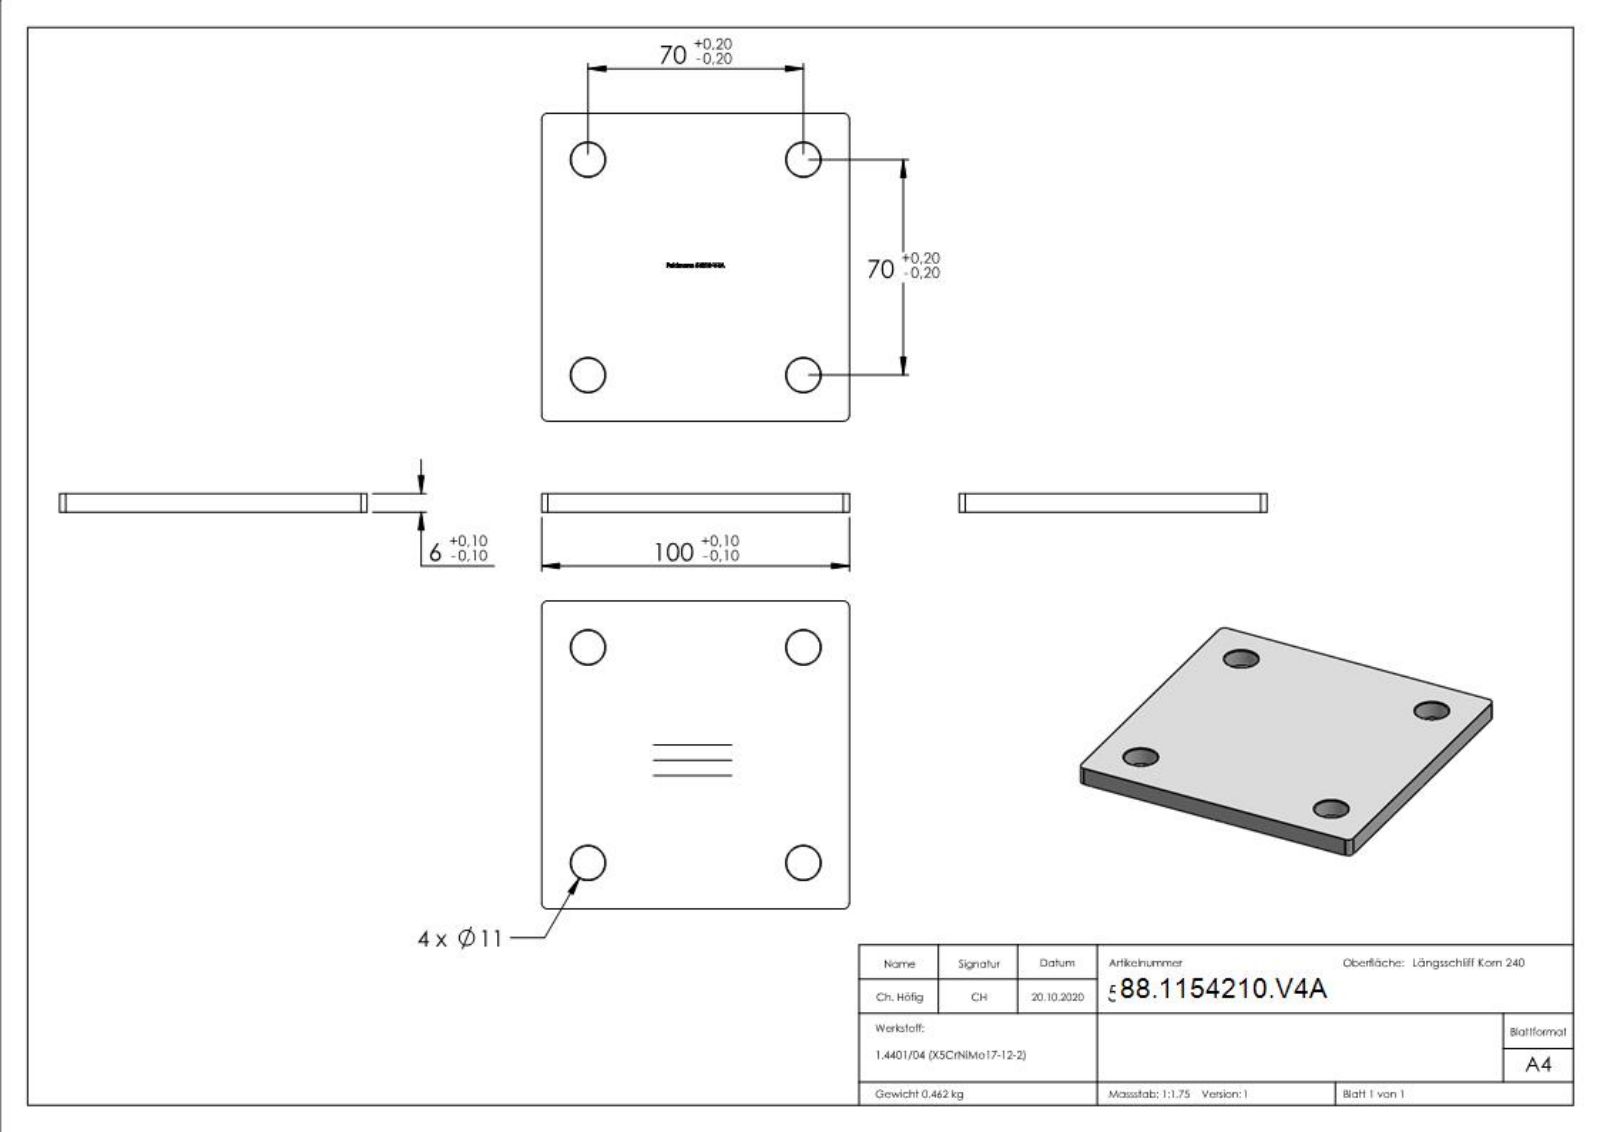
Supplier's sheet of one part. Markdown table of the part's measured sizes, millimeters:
| quantity | value |
| --- | --- |
| part name | 54210-V4A |
| STEP written by | SolidWorks 2018 (CONFIG_CONTROL_DESIGN) |
| units | millimeters |
| bodies | 1 solid, 249 faces (150 planar, 12 cylindrical, 87 other) |
| overall size | 100 × 100 × 6 |
| volume | 57 689 mm³ |
| surface area | 22 411 mm² |
| round holes (diameter × count) | 11 × 4 |
| partial cylindrical surfaces (radius × count) | 2 × 4 |
| main face-to-face distances | 6, 100, 5.9, 50, 0.88, 10.74, 2.97, 0.44, 2.01, 12.75 |
| hole center spacings | 70, 98.99 |
